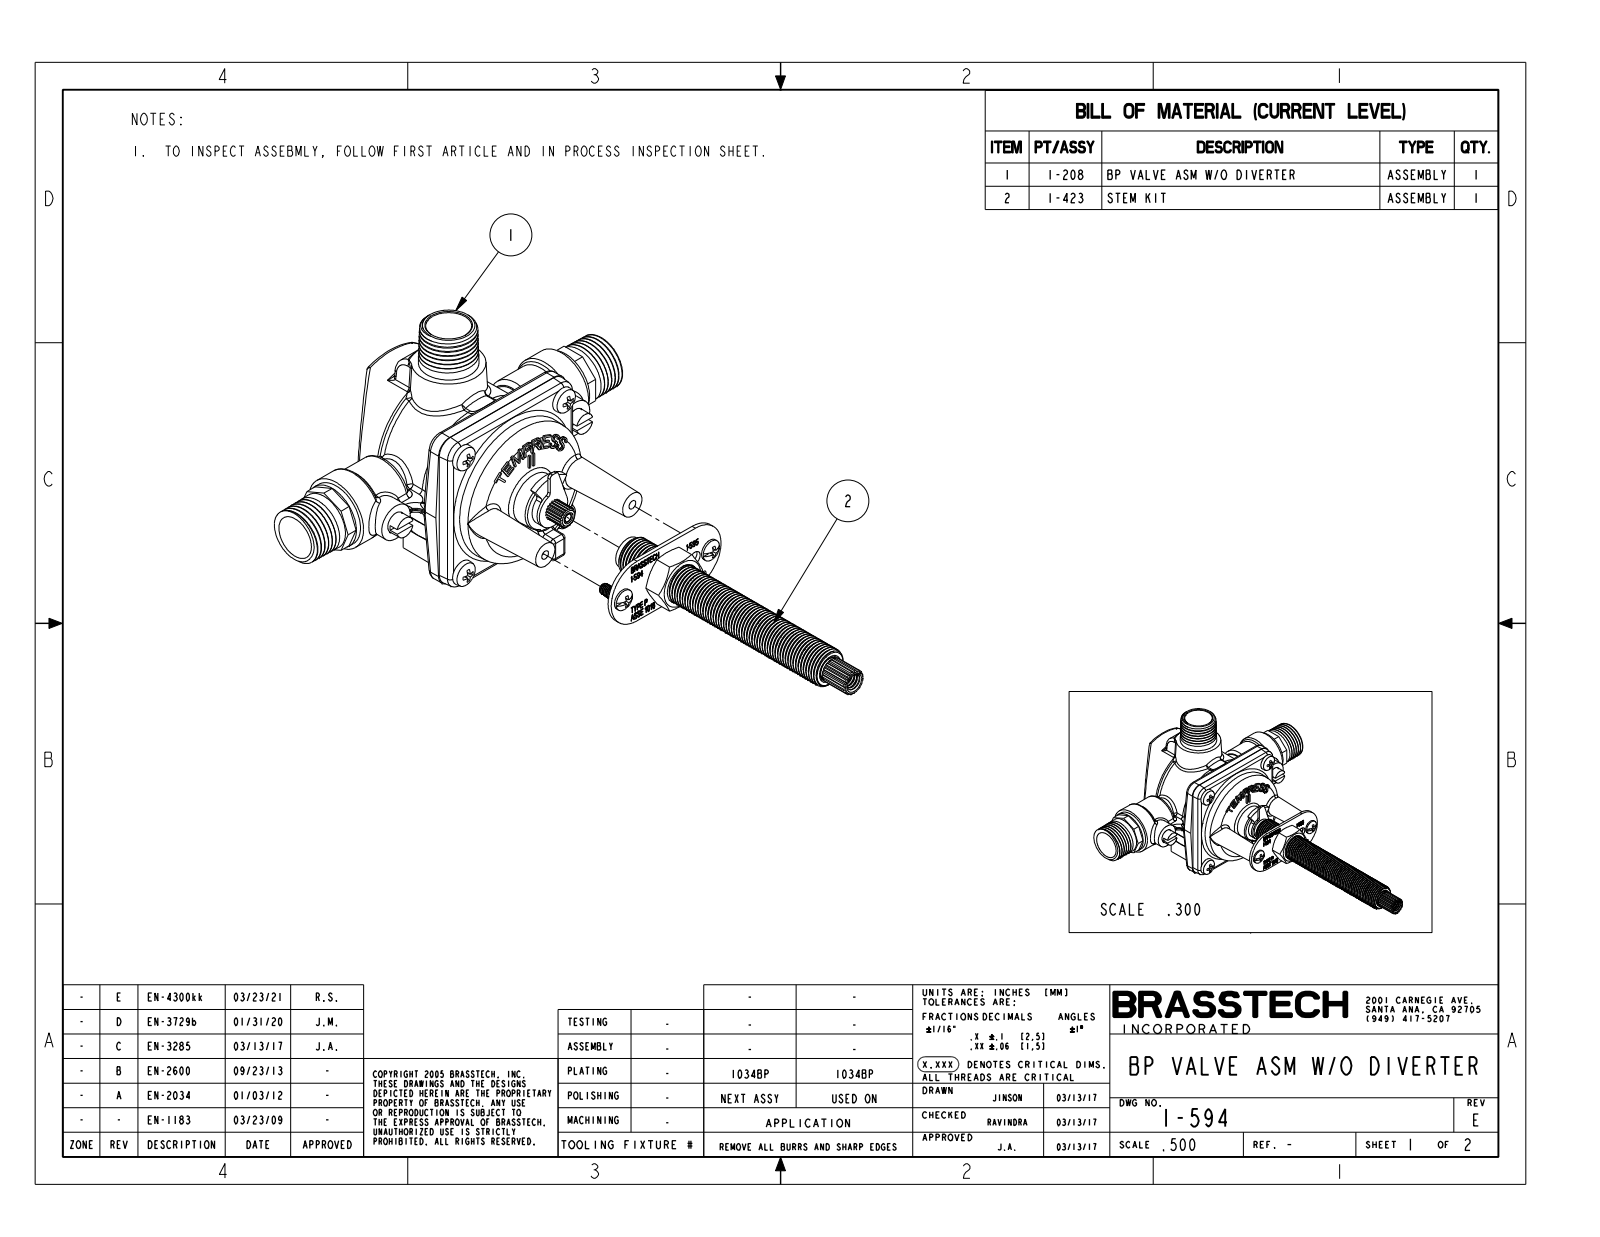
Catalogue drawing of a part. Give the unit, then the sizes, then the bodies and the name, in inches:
Units: inches
Overall size (bounding box): 7.655 × 5.961 × 3.629
Round holes (diameter × count): ⌀0.171 ×4, ⌀0.237 ×4, ⌀0.315 ×2, ⌀0.63 ×2, ⌀0.2 ×1, ⌀0.202 ×1, ⌀0.23 ×1, ⌀0.398 ×1, ⌀0.51 ×1, ⌀0.85 ×1, ⌀0.98 ×1
Round bosses / shafts (diameter × count): ⌀0.19 ×4, ⌀0.551 ×2, ⌀0.315 ×2, ⌀0.313 ×2, ⌀0.217 ×2, ⌀2.22 ×1, ⌀1.063 ×1, ⌀1.024 ×1
Partial cylindrical surfaces — rounded edges, fillets, slot ends (radius × count): R0.063 ×41, R0.05 ×17, R0.06 ×10, R0.217 ×4, R0.039 ×2, R0.065 ×2, R0.307 ×2, R0.5 ×2
Main face-to-face distances: 1.187, 0.062, 1.125, 0.079, 0.36, 1.485, 1.547, 0.315, 1.12, 0.077
Hole centre spacings: 1.241, 1.375, 1.945, 2.885, 1.744, 2.75, 0.56, 1.053
Volume: 15.84 in³ · Surface area: 81.13 in²
Bodies: 1 solid, 2336 faces (977 planar, 470 cylindrical, 889 other)
Part name (STEP PRODUCT): 1-594_SW0002
STEP written by: CREO PARAMETRIC BY PTC INC, 2018400 (AUTOMOTIVE_DESIGN)
